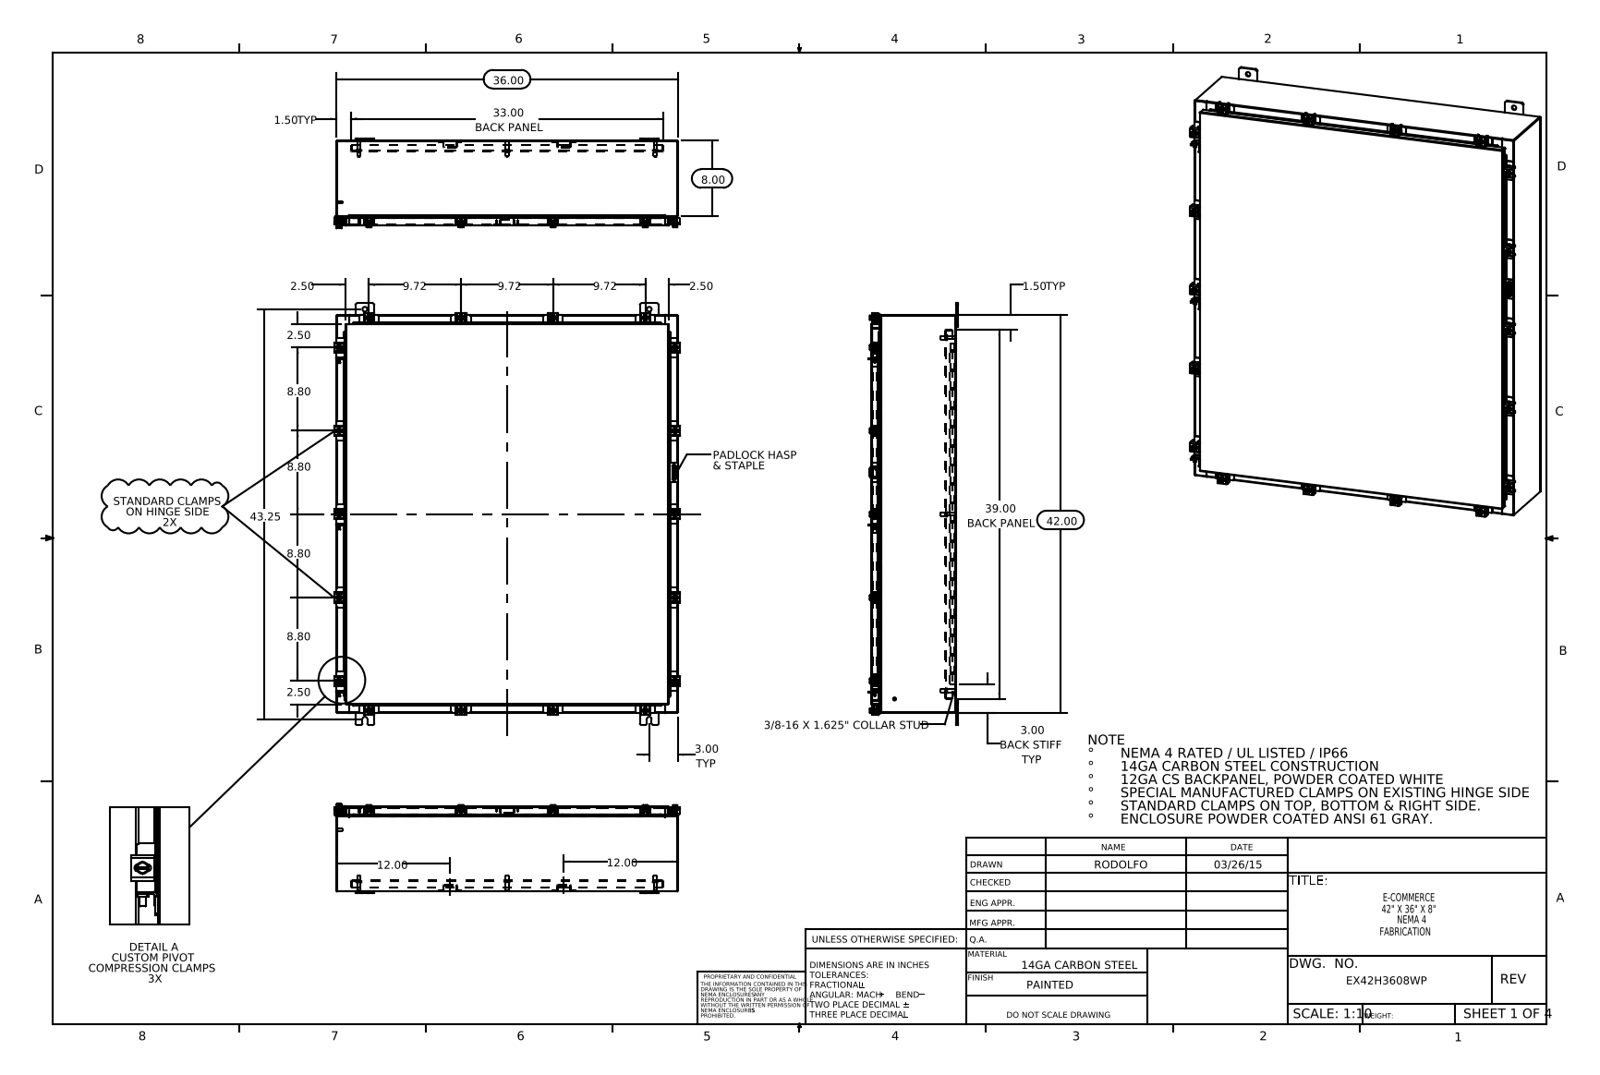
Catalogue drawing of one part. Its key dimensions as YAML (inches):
part_name: "EX42H3608WP Door Stiffener; N-WMT04X30402202210-00 22104005_DEFAULT; EX42H3608WP Enclosure Stiffener; 10_30 CD Stud (+8 more)"
step_written_by: "SolidWorks 2014 (CONFIG_CONTROL_DESIGN)"
units: inches
bodies: {solids: 126, faces: 3106, planar: 1613, cylindrical: 1195, other: 298}
overall_size: [44.5, 36.421, 9.453]
volume: 530.7
surface_area: 13133
round_holes:
  - {diameter: 0.213, count: 18}
  - {diameter: 0.26, count: 18}
  - {diameter: 0.5, count: 12}
  - {diameter: 0.25, count: 7}
  - {diameter: 0.125, count: 1}
round_bosses_or_shafts:
  - {diameter: 0.5, count: 18}
  - {diameter: 0.25, count: 18}
  - {diameter: 0.399, count: 15}
  - {diameter: 0.625, count: 8}
  - {diameter: 0.375, count: 8}
  - {diameter: 0.33, count: 8}
  - {diameter: 0.157, count: 6}
  - {diameter: 0.14, count: 6}
partial_cylinders:
  - {radius: 0.06, count: 76}
  - {radius: 0.013, count: 38}
  - {radius: 0.141, count: 36}
  - {radius: 0.088, count: 34}
  - {radius: 0.12, count: 33}
  - {radius: 0.09, count: 27}
  - {radius: 0.05, count: 25}
  - {radius: 0.145, count: 24}
face_to_face_distances: [0.075, 8.9, 8.826, 8.975, 0.104, 1, 1.075, 7.826, 7.9, 1.179]
hole_center_spacings: [1.969, 2.347, 4.44, 13.972, 14.729, 16.126, 16.624, 17]
